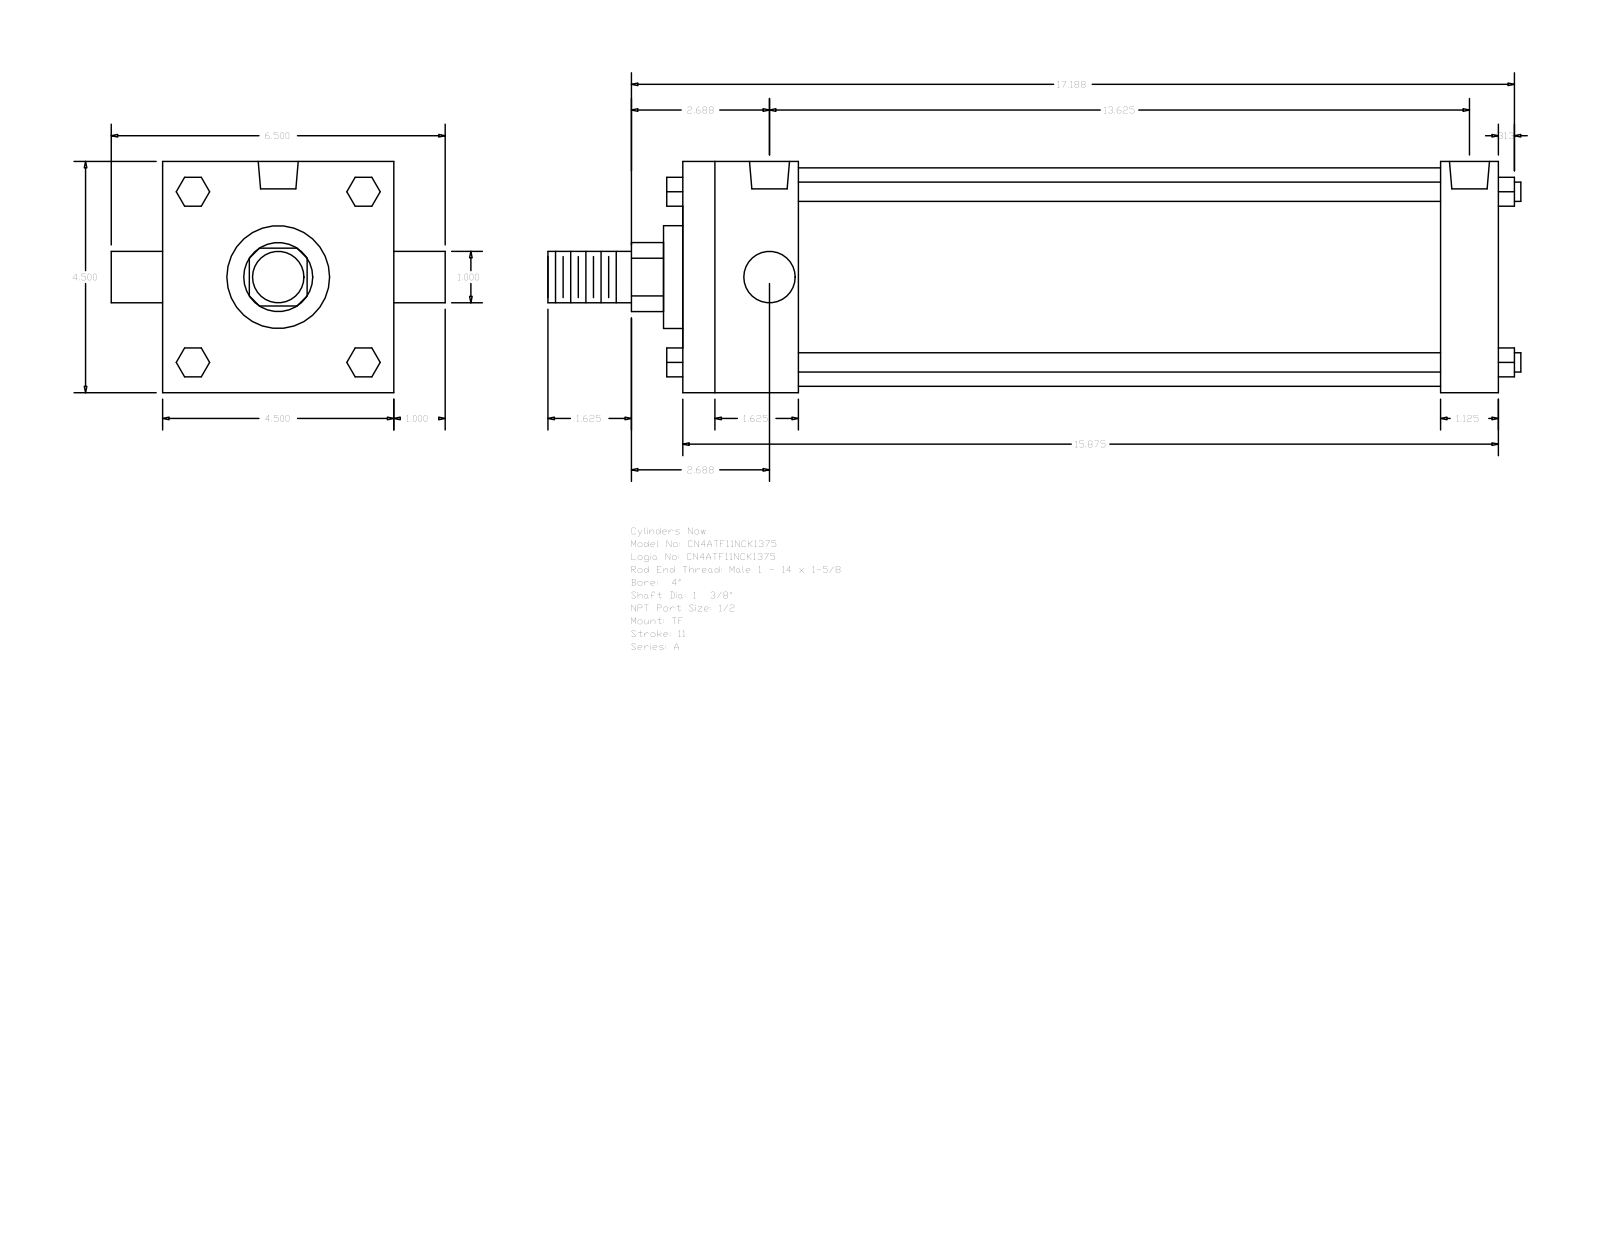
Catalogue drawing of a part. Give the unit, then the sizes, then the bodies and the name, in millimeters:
Units: millimetres
Overall size (bounding box): 481.01 × 165.1 × 114.3
Round holes (diameter × count): ⌀8.73 ×3, ⌀19.77 ×2
Round bosses / shafts (diameter × count): ⌀9.53 ×4, ⌀25.4 ×2, ⌀107.95 ×1, ⌀50.8 ×1, ⌀34.92 ×1
Partial cylindrical surfaces — rounded edges, fillets, slot ends (radius × count): R17.06 ×1
Main face-to-face distances: 114.3, 403.22, 57.15, 374.65, 28.57, 317.5, 346.07, 66.67, 14.29, 25.4
Hole centre spacings: 3.18, 342.9, 339.72, 346.08
Bodies: 0 solids, 120 faces (92 planar, 28 cylindrical, 0 other)
Part name (STEP PRODUCT): A_TF__0400_1.375
STEP written by: GSSL Pune (CONFIG_CONTROL_DESIGN)
